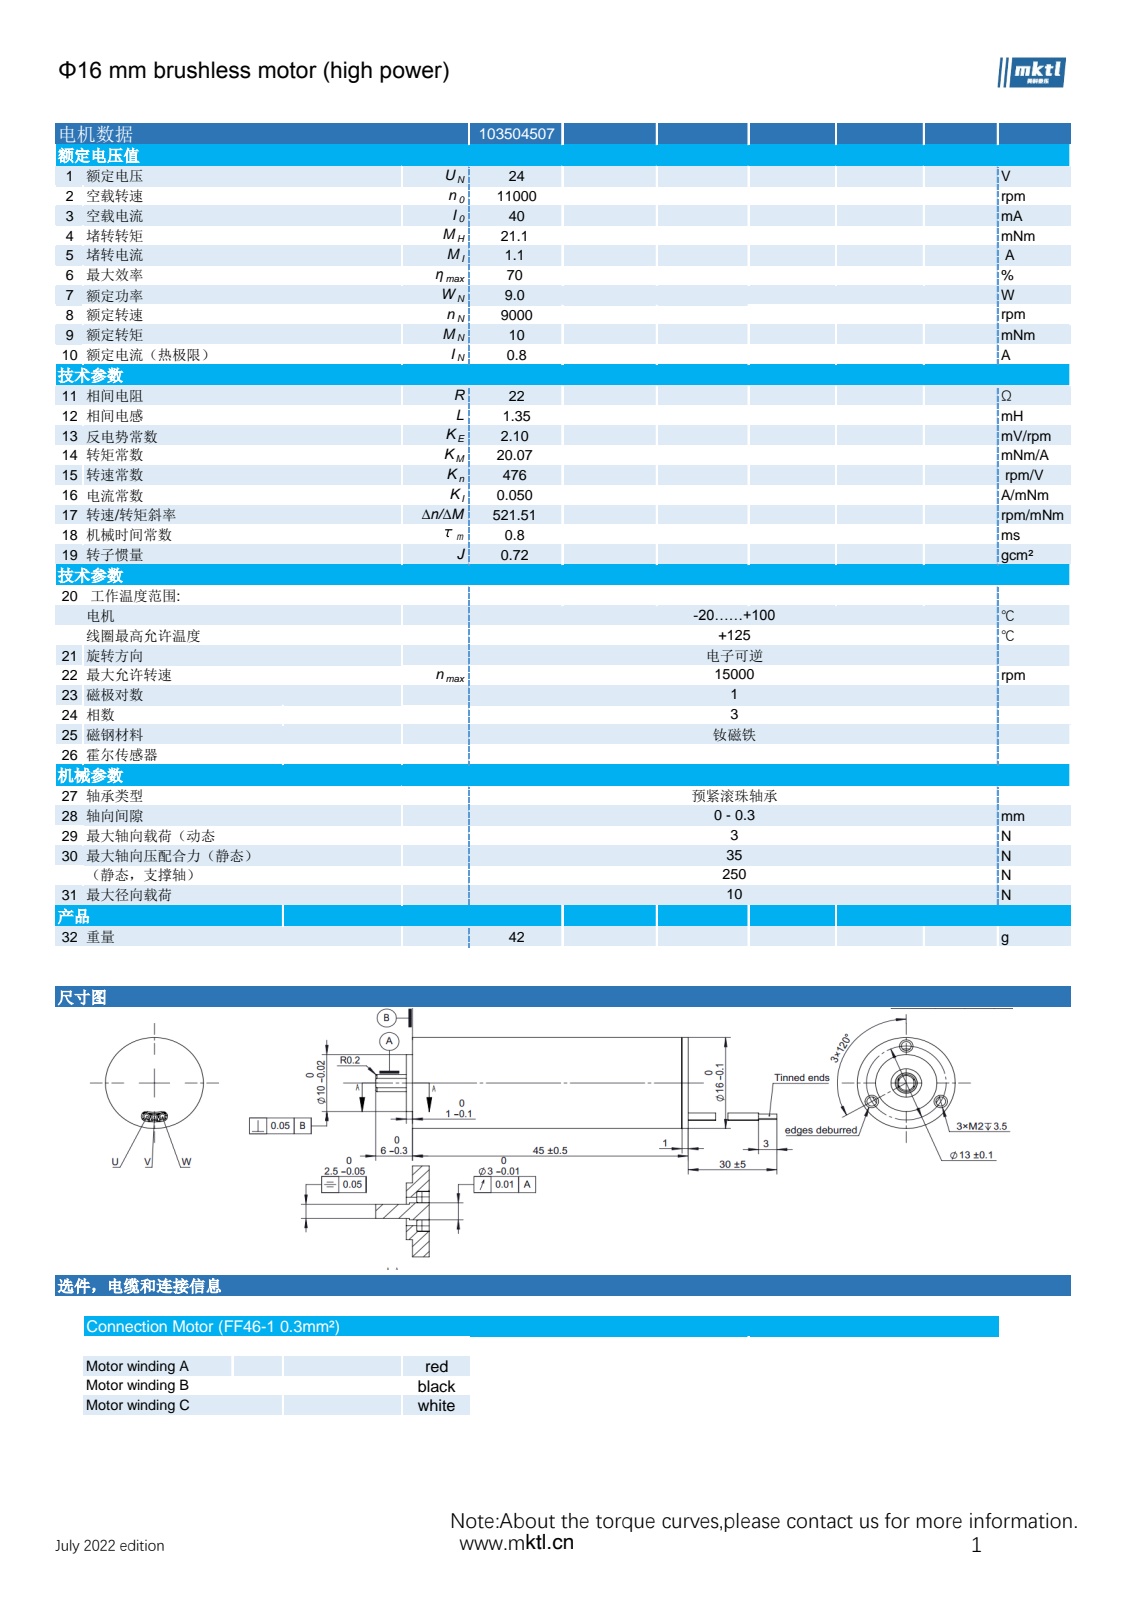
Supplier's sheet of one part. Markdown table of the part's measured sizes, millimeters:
| quantity | value |
| --- | --- |
| part name | 103504507 |
| STEP written by | SolidWorks 2025 (AUTOMOTIVE_DESIGN) |
| units | millimeters |
| bodies | 189 solids, 1319 faces (444 planar, 822 cylindrical, 53 other) |
| overall size | 65.5 × 16 × 16 |
| volume | 8 144 mm³ |
| surface area | 39 870 mm² |
| round holes (diameter × count) | 0.8 × 3, 1.2 × 3, 1.6 × 3, 3 × 1, 3.1 × 1, 5 × 1, 7 × 1, 8.1 × 1, 8.8 × 1, 10.8 × 1, 11 × 1, 11.2 × 1 |
| round bosses / shafts (diameter × count) | 1.2 × 3, 0.8 × 3, 0.3 × 3, 16 × 1, 15 × 1, 14.9 × 1, 10 × 1, 7.5 × 1 |
| partial cylindrical surfaces (radius × count) | 0.85 × 2, 0.95 × 2, 1.25 × 2, 4.75 × 1, 5.15 × 1, 5.65 × 1, 6.5 × 1, 6.85 × 1 |
| main face-to-face distances | 1, 0.4, 0.6, 0.8, 2, 25.6, 1.4, 1.2, 24.6, 3 |
| hole center spacings | 6.5, 6.8, 11.26, 1.42, 5.42, 6.66, 7.82, 13.23 |
